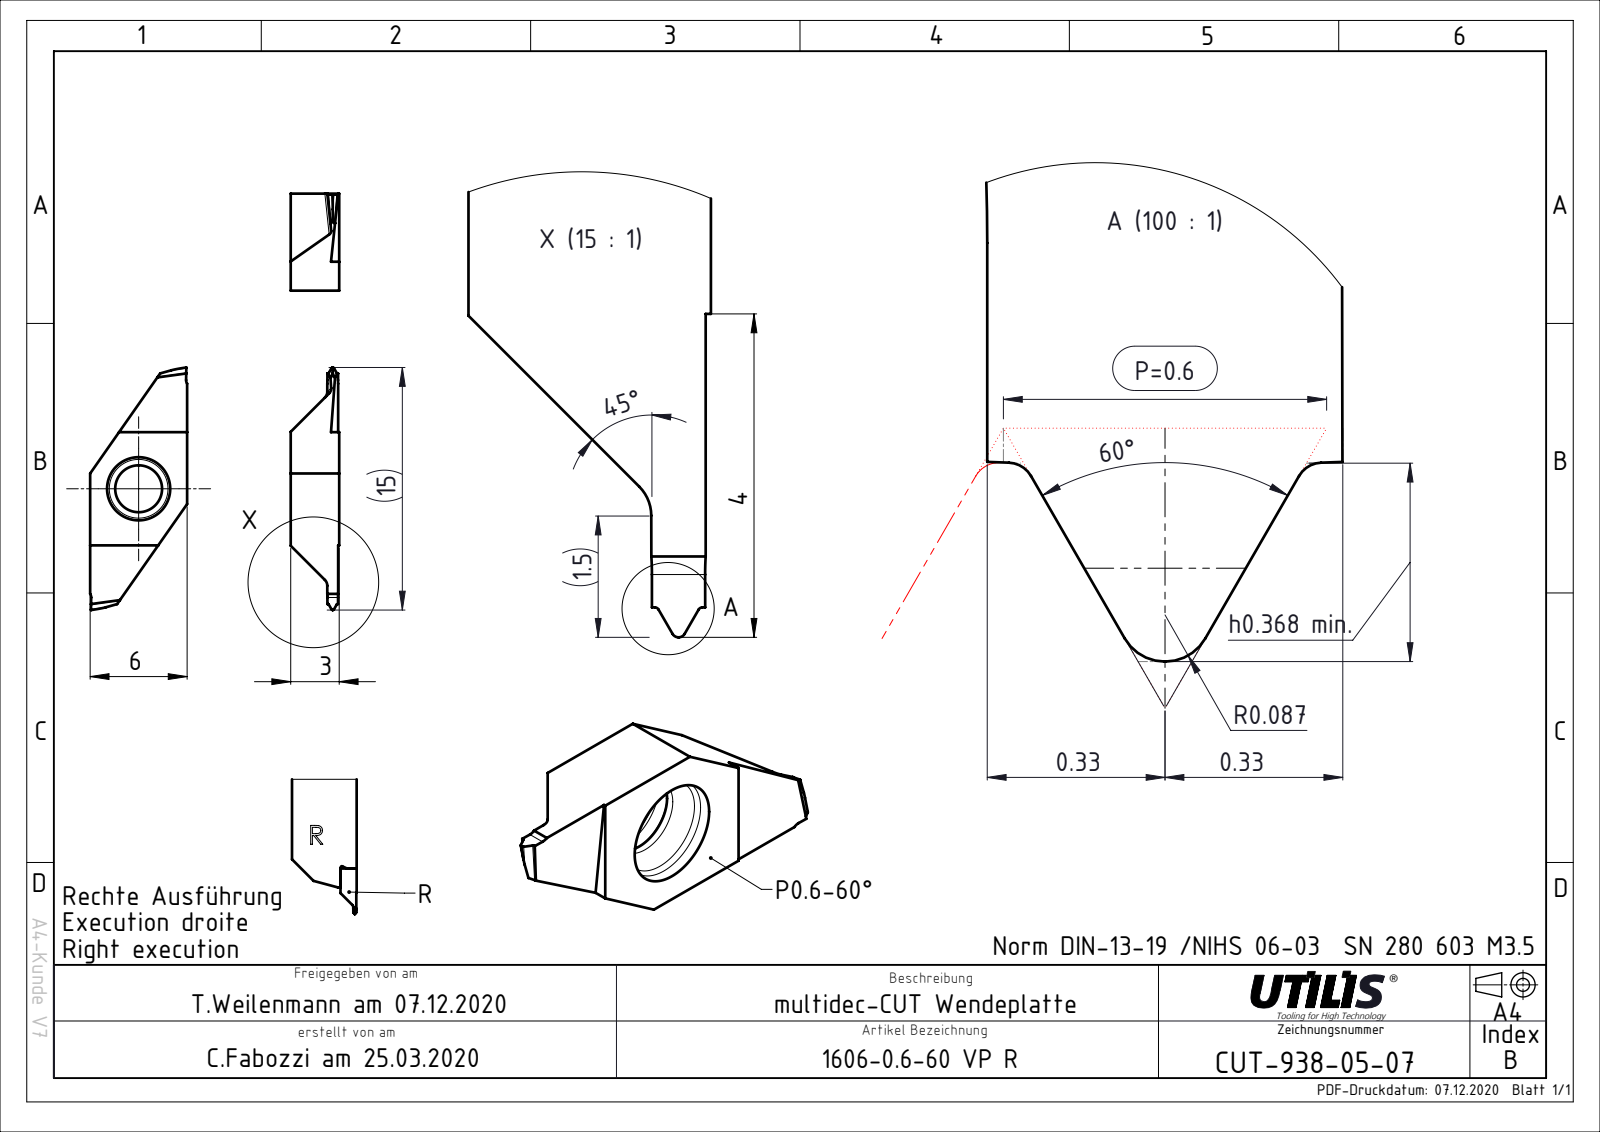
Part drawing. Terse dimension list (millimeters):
name: CUT-938-05; ASME Y14.5
written by: FormatWorks Professional (AP242_MANAGED_MODEL_BASED_3D_ENGINEERING_MIM_LF)
unit: mm
bodies: 1 solid, 42 faces (24 planar, 14 cylindrical, 4 other)
size: 15 × 6 × 3
volume: 126 mm³; area: 210 mm²
holes: 1× ⌀2.9
rounds: 2× R0.5
face distances: 6, 3, 0.51, 9, 11.19, 11.2, 12, 7, 12.79, 12.8
